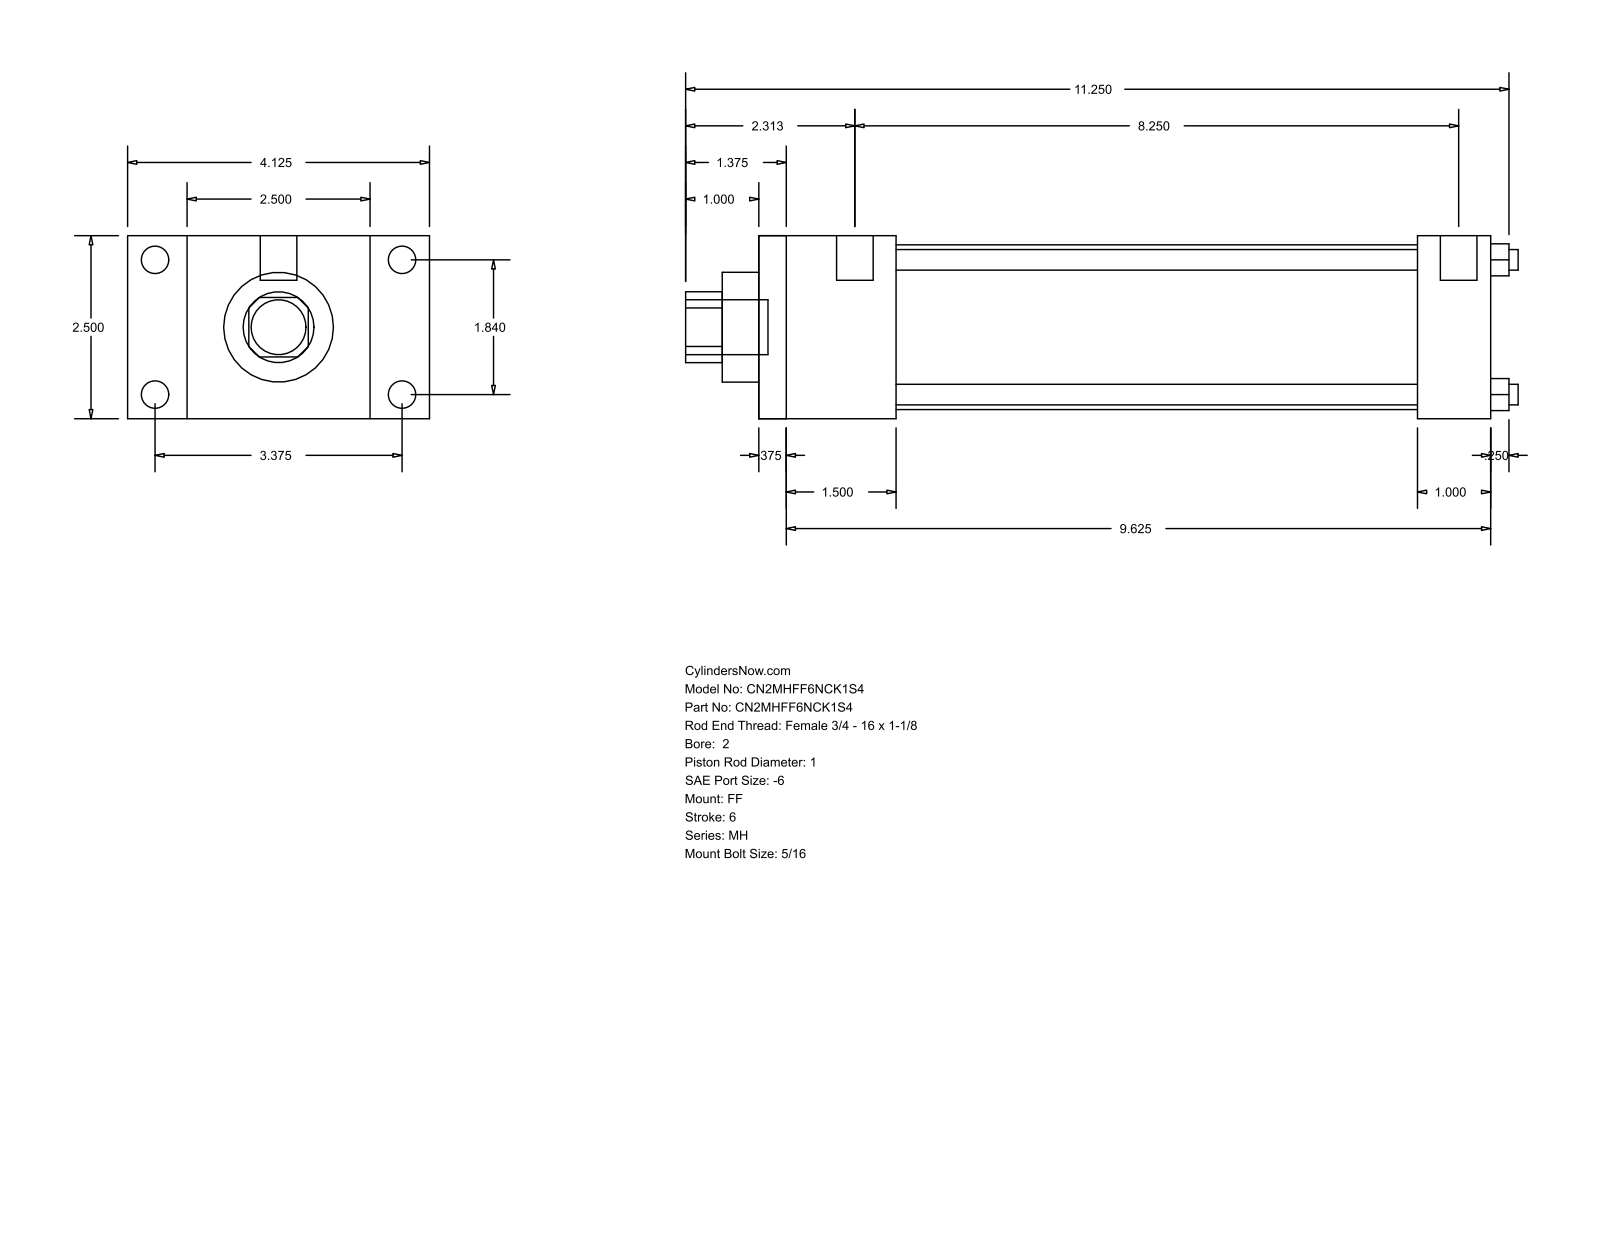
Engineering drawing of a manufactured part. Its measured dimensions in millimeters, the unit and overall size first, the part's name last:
Units: millimetres
Overall size (bounding box): 288.93 × 104.78 × 63.5
Round holes (diameter × count): ⌀7.14 ×4, ⌀25.4 ×1, ⌀38.1 ×1, ⌀57.15 ×1
Round bosses / shafts (diameter × count): ⌀9.53 ×4, ⌀5.56 ×4, ⌀12.7 ×2, ⌀19.05 ×1
Partial cylindrical surfaces — rounded edges, fillets, slot ends (radius × count): R12.29 ×1
Main face-to-face distances: 63.5, 254, 9.52, 244.48, 20.64, 25.4, 47.63, 228.6, 38.11, 219.08
Hole centre spacings: 33.05, 46.74, 66.1
Bodies: 0 solids, 92 faces (64 planar, 28 cylindrical, 0 other)
Part name (STEP PRODUCT): MH_FF__0200_1
STEP written by: GSSL Pune (CONFIG_CONTROL_DESIGN)
